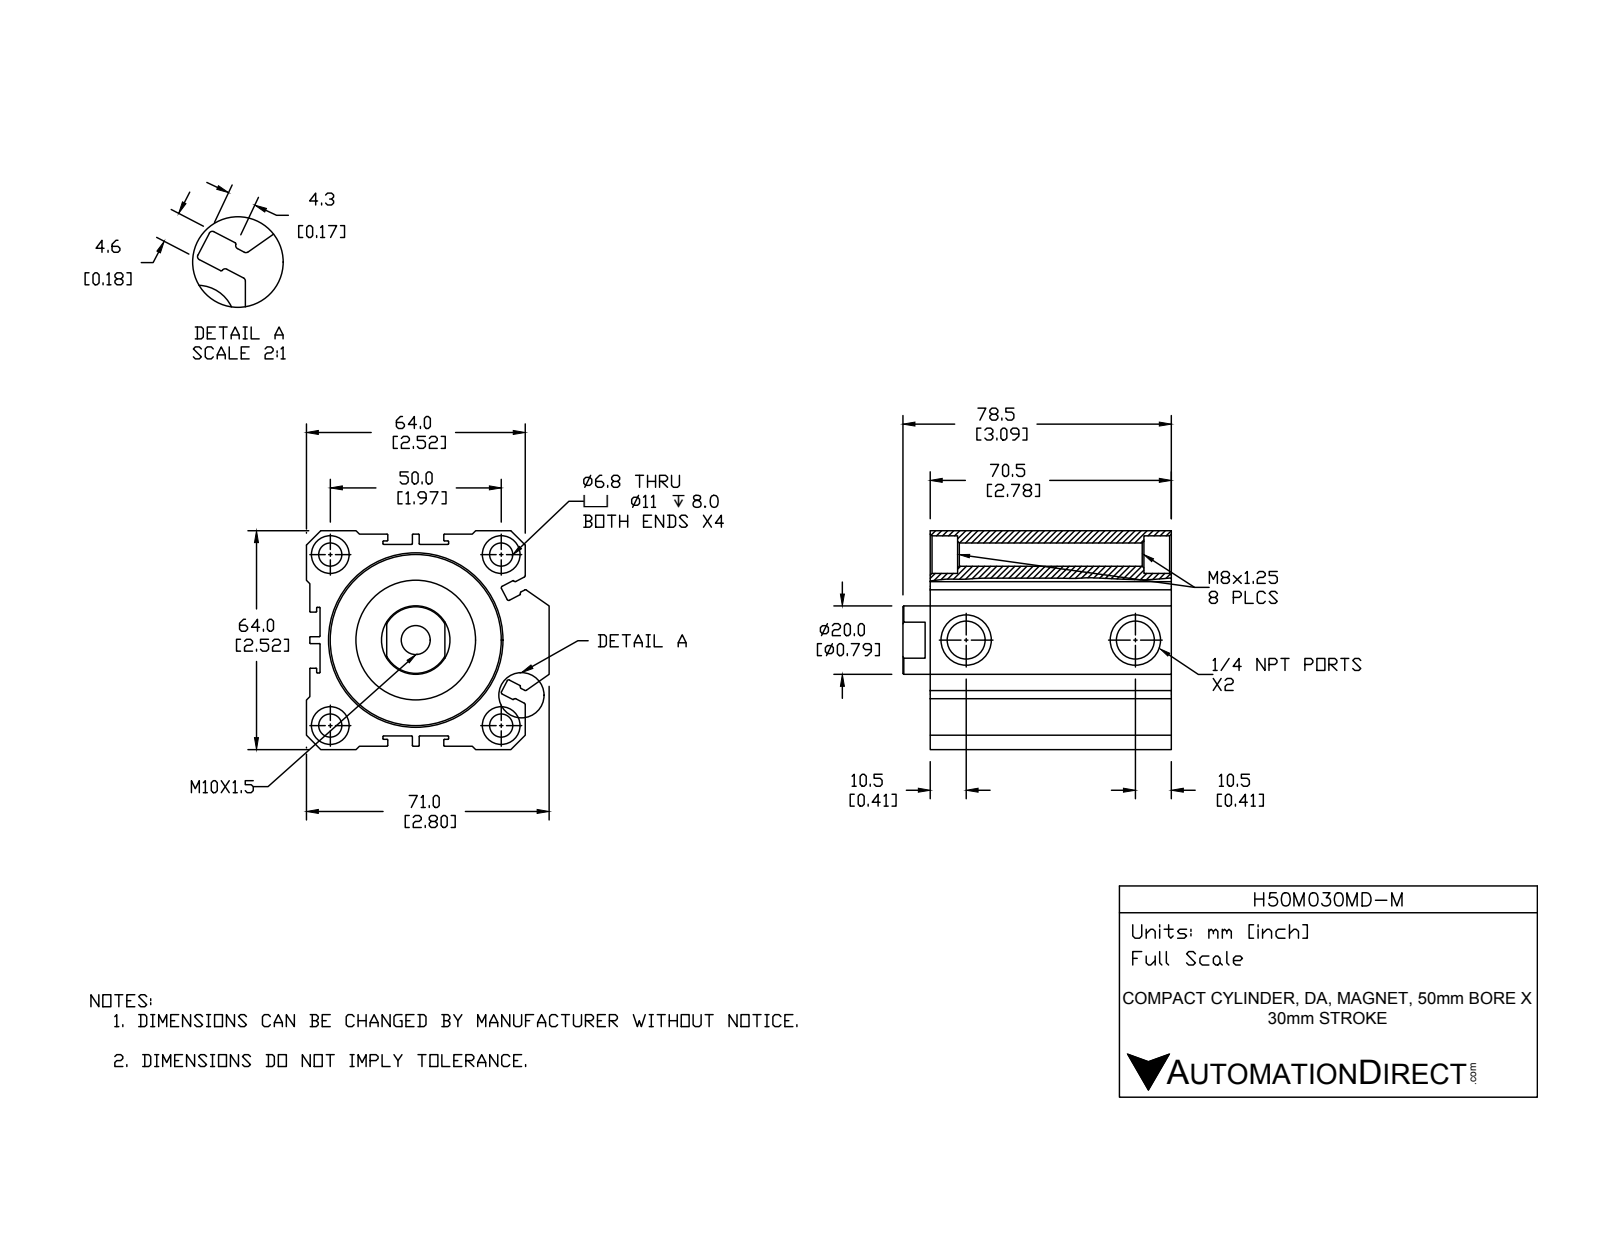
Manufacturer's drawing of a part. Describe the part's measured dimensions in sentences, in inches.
The part is named "H50M030MD-M-PISTON; H50M030MD-M; H50M030MD-M-BODY". Its 3-D file was written by "SolidWorks 2015 (CONFIG_CONTROL_DESIGN)". It is 2 solids with 255 faces: 99 planar, 103 cylindrical and 53 other. Overall it measures 3.091 by 2.795 by 2.52 inches. Its volume is 12.24 cubic inches and its surface area 98.05 square inches. Round holes: 4 of diameter 0.268, 4 of diameter 0.433, 2 of diameter 0.438, 1 of diameter 0.335, 1 of diameter 0.787, 1 of diameter 1.417, 1 of diameter 1.969. Round bosses or shafts: 1 of diameter 1.378, 1 of diameter 1.22. Partial cylindrical surfaces (rounded edges, fillets, slot ends): 40 of radius 0.008, 12 of radius 0.02. The main face-to-face distances are 2.48, 2.362, 0.157, 0.039, 1.181, 0.118, 2.323, 2.52, 0.276, 0.079. The hole center spacings are 1.392, 1.969, 2.784, 1.949.
